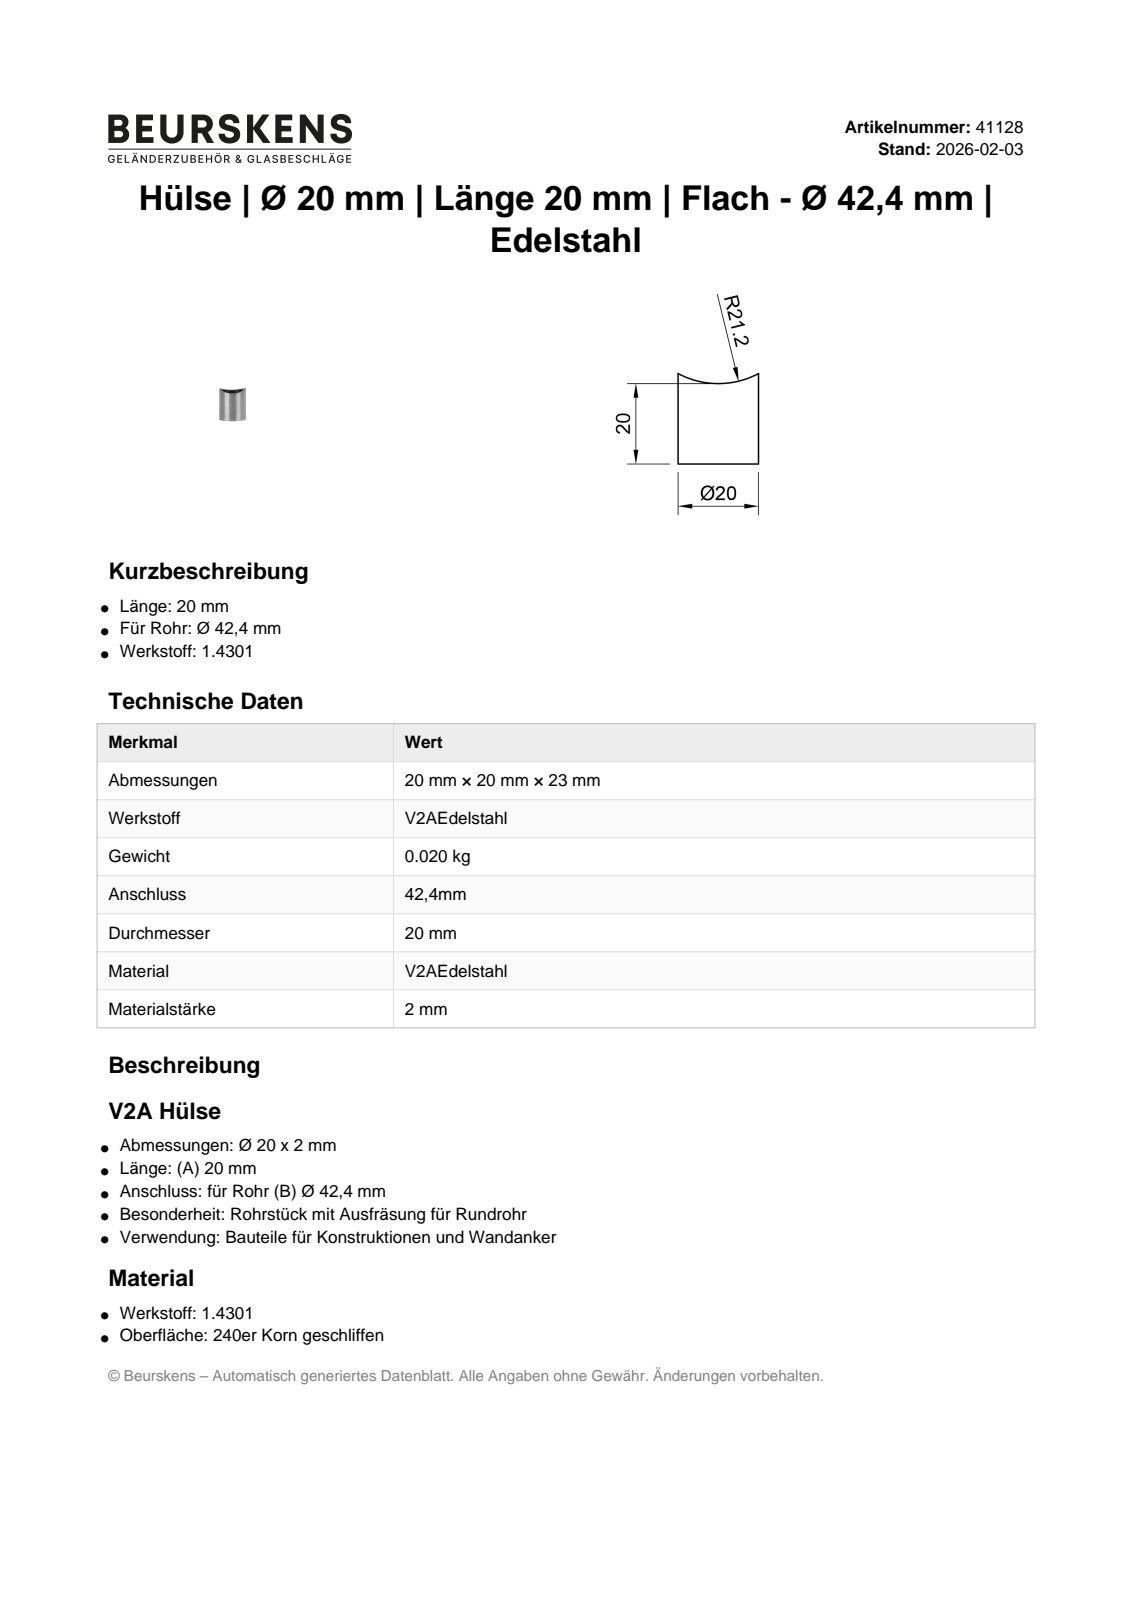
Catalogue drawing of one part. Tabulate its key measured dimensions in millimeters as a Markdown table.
| quantity | value |
| --- | --- |
| part name | 41128 |
| STEP written by | Autodesk Inventor 2022 (AUTOMOTIVE_DESIGN) |
| units | millimeters |
| bodies | 1 solid, 4 faces (1 planar, 3 cylindrical, 0 other) |
| overall size | 22.51 × 20 × 20 |
| volume | 1 260 mm³ |
| surface area | 2 644 mm² |
| round holes (diameter × count) | 18 × 1 |
| round bosses / shafts (diameter × count) | 20 × 1 |
| partial cylindrical surfaces (radius × count) | 21.2 × 1 |
